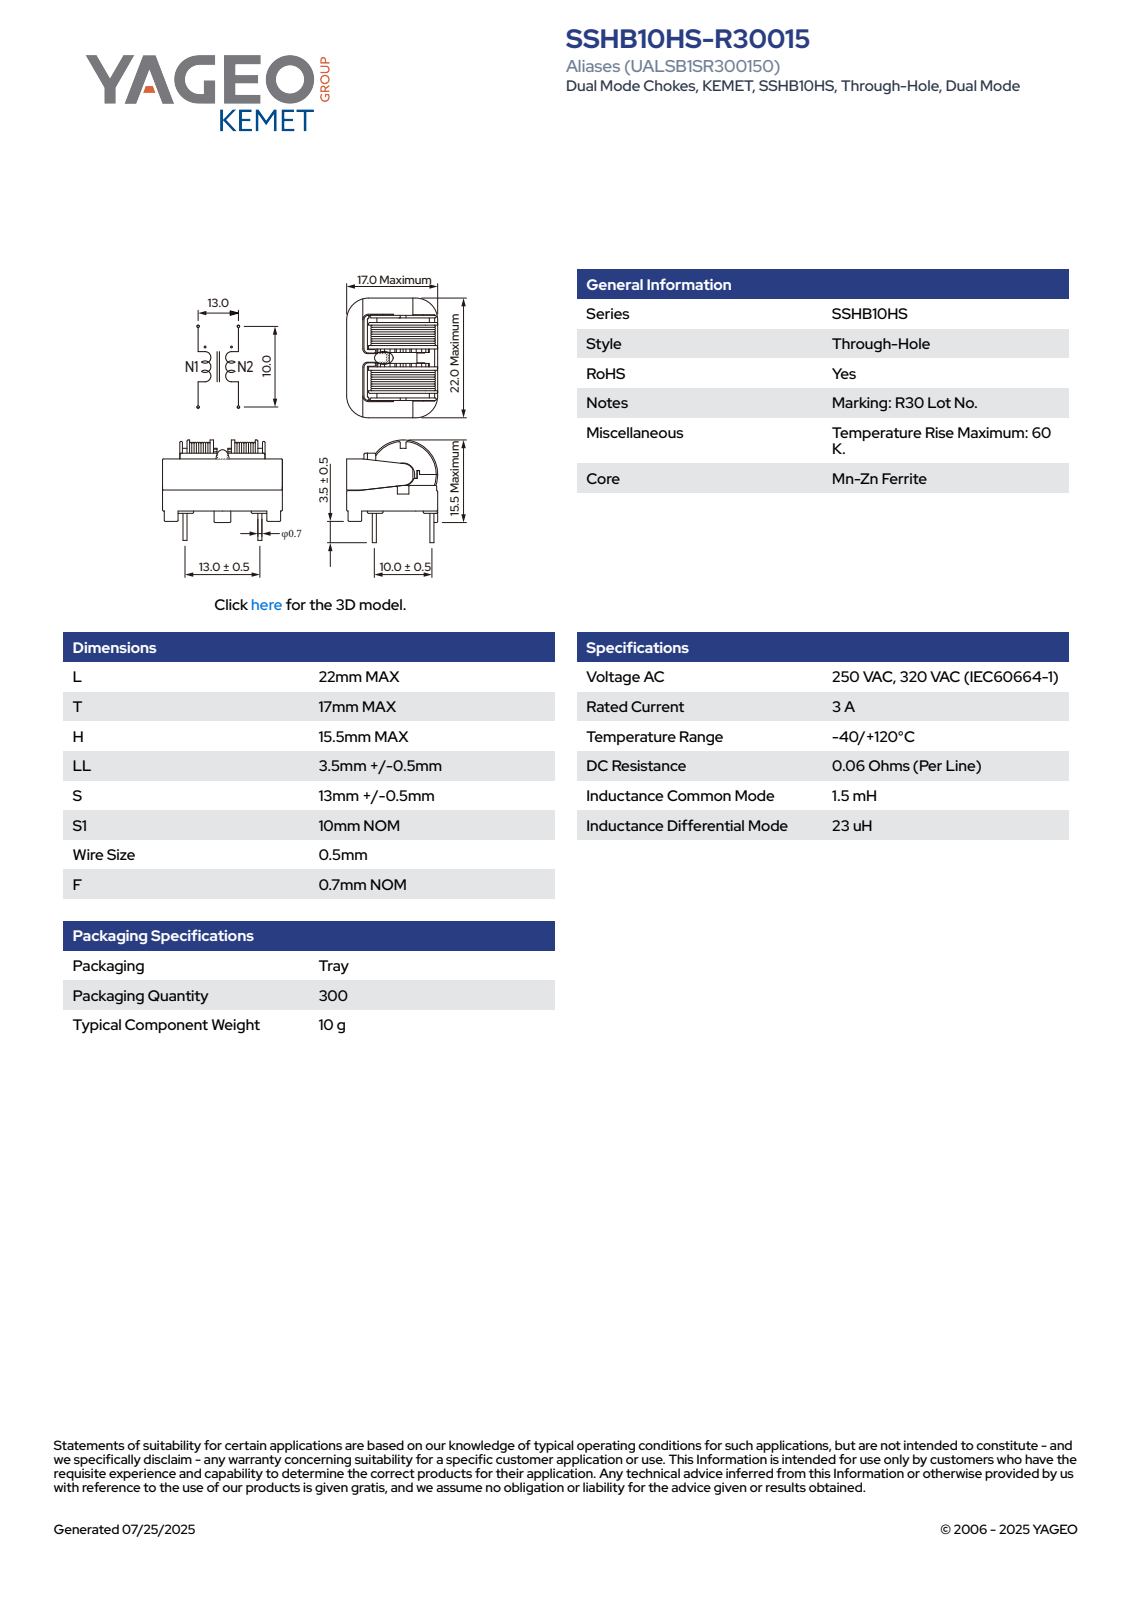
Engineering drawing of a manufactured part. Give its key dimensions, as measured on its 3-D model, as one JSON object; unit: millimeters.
{"part_name": "SSHB10HS(MAX-LOGO)", "step_written_by": "SolidWorks 2018 (AUTOMOTIVE_DESIGN)", "units": "millimeters", "bodies": {"solids": 1, "faces": 425, "planar": 294, "cylindrical": 99, "other": 32}, "overall_size": [22, 19, 17], "volume_mm3": 2987, "surface_area_mm2": 3442, "round_holes": [[4.1, 1]], "round_bosses_or_shafts": [[0.7, 4], [12, 1], [11.5, 1], [9.1, 1], [6.3, 1], [3.8, 1]], "partial_cylinders_radius": [[0.2, 26], [0.8, 6], [3.8, 4], [1, 2], [5, 2], [5, 2], [1.8, 1], [3.6, 1]], "face_to_face_distances": [8.95, 0.6, 8.4, 3.6, 18.4, 2.39, 5.86, 8.94, 4.9, 14.8]}
